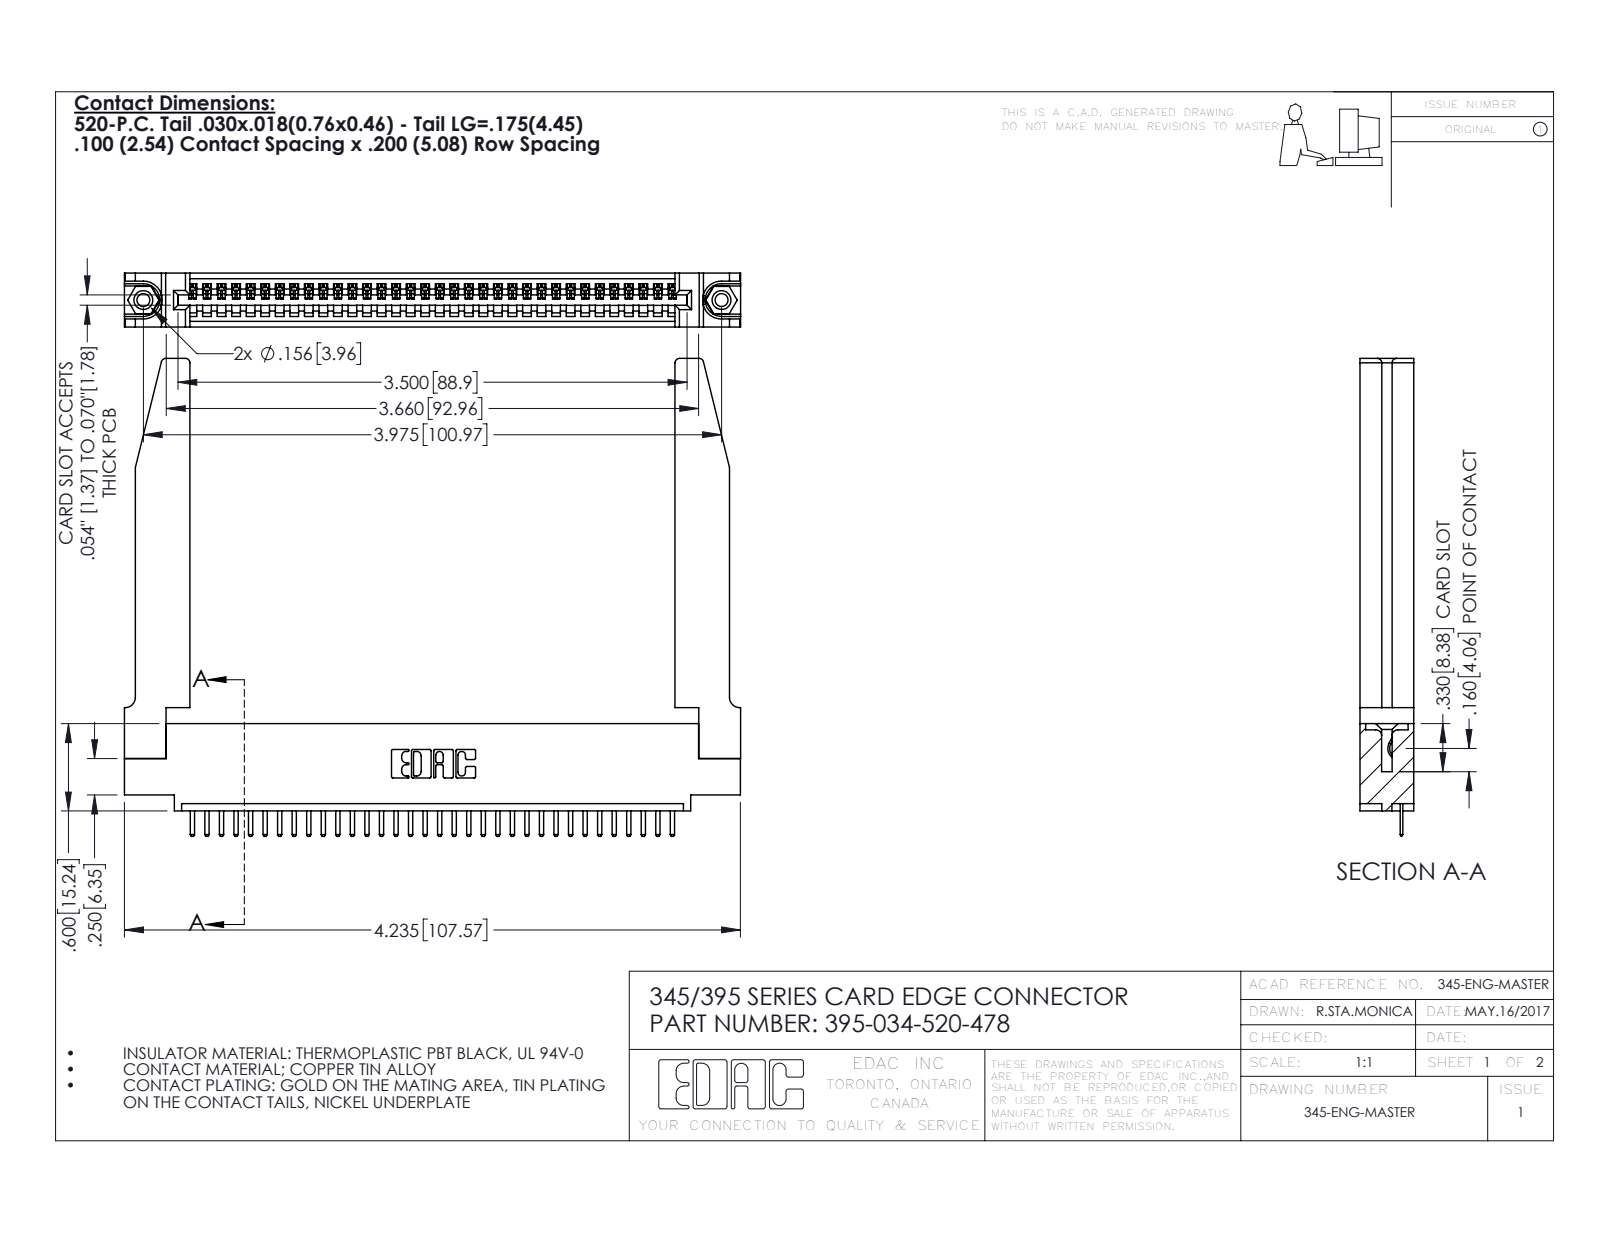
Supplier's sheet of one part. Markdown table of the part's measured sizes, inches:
| quantity | value |
| --- | --- |
| part name | 345-250-001_345-250-001-102; 395-034-520-478; 345-220-078_345-220-078; 345-292-001_345-293-120 (+1 more) |
| STEP written by | SolidWorks 2016 (CONFIG_CONTROL_DESIGN) |
| units | inches |
| bodies | 39 solids, 2472 faces (1654 planar, 766 cylindrical, 52 other) |
| overall size | 4.236 × 3.285 × 0.37 |
| volume | 1.083 in³ |
| surface area | 30.64 in² |
| round holes (diameter × count) | 0.089 × 2, 0.125 × 2, 0.156 × 2, 0.064 × 1 |
| round bosses / shafts (diameter × count) | 0.155 × 2 |
| partial cylindrical surfaces (radius × count) | 0.01 × 70, 0.006 × 68, 0.01 × 22, 0.03 × 8, 0.007 × 6, 0.031 × 6, 0.026 × 3, 0.031 × 2 |
| main face-to-face distances | 0.37, 0.072, 0.298, 0.2, 0.098, 0.272, 0.025, 0.225, 0.15, 0.148 |
| hole center spacings | 0.27, 3.74, 3.975 |
